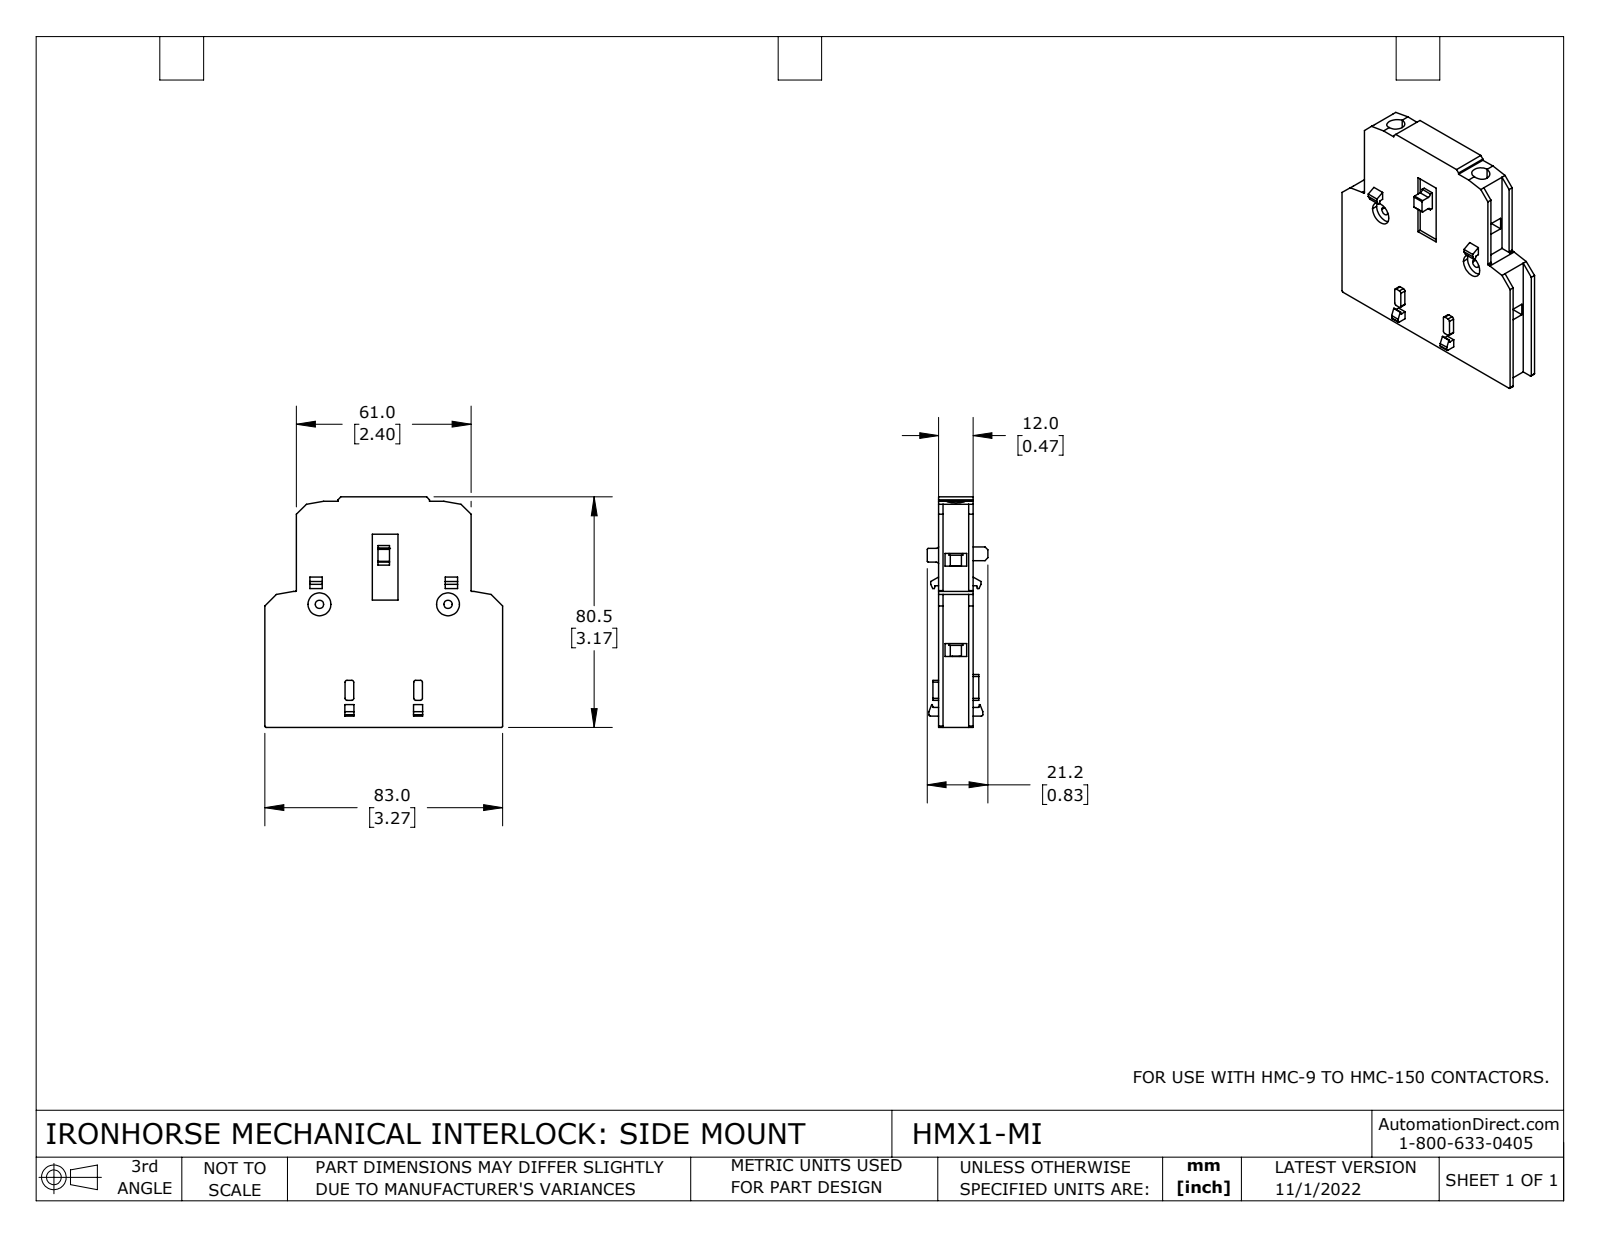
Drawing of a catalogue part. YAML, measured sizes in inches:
part_name: "HMX1-MI"
step_written_by: "SolidWorks 2021 (CONFIG_CONTROL_DESIGN)"
units: inches
bodies: {solids: 9, faces: 378, planar: 252, cylindrical: 90, other: 36}
overall_size: [3.268, 3.169, 0.835]
volume: 3.873
surface_area: 31.55
round_holes:
  - {diameter: 0.114, count: 2}
  - {diameter: 0.157, count: 2}
  - {diameter: 0.248, count: 2}
  - {diameter: 0.315, count: 2}
round_bosses_or_shafts:
  - {diameter: 0.189, count: 4}
  - {diameter: 0.154, count: 4}
  - {diameter: 0.091, count: 4}
  - {diameter: 0.079, count: 2}
partial_cylinders:
  - {radius: 0.028, count: 12}
  - {radius: 0.012, count: 4}
  - {radius: 0.02, count: 4}
  - {radius: 0.116, count: 4}
  - {radius: 0.039, count: 2}
face_to_face_distances: [0.472, 0.413, 0.059, 0.354, 0.043, 2.539, 0.386, 2.953, 1.24, 0.157]
hole_center_spacings: [1.143, 2.281, 1.654, 1.768, 2.205]
